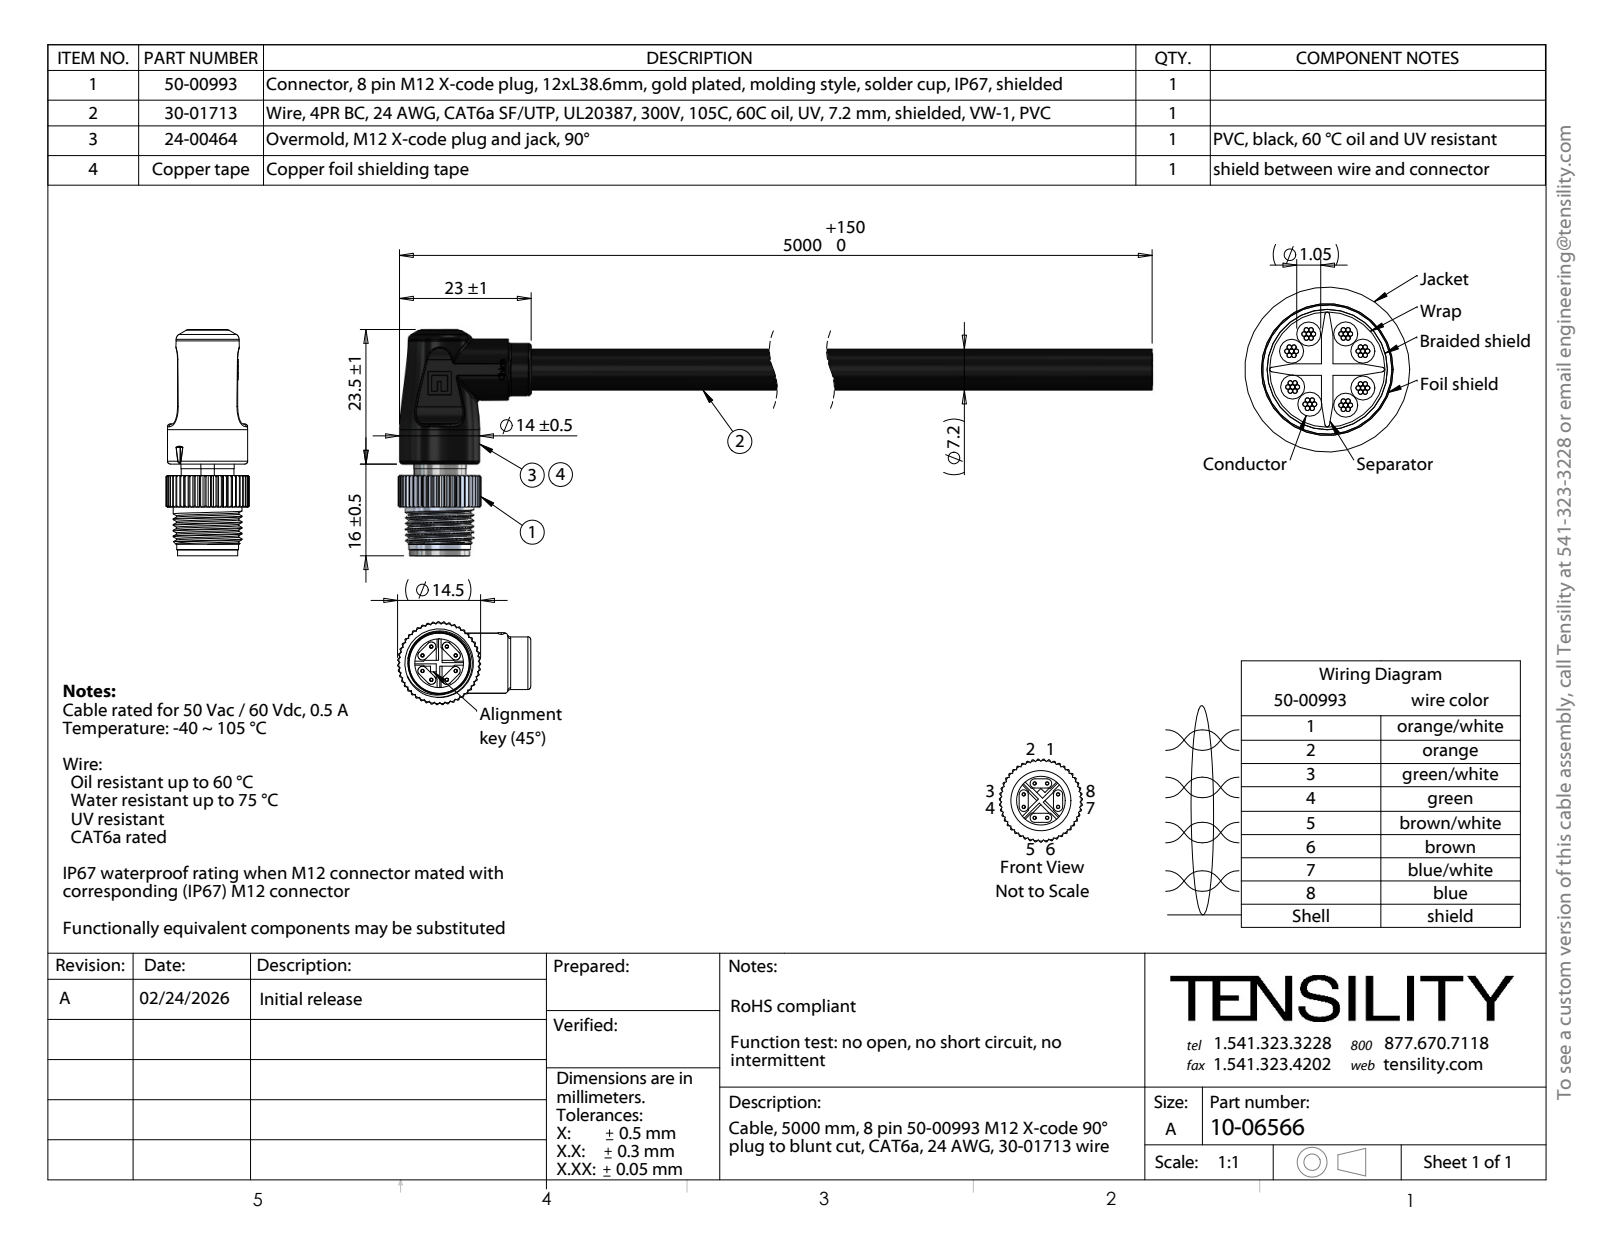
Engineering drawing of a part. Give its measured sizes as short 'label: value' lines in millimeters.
name: 50-00993-03; 50-00993-02; 30-01713_blunt cut; 50-00993-01_STEP (+5 more)
written by: SolidWorks 2025 (CONFIG_CONTROL_DESIGN)
unit: mm
bodies: 85 solids, 1492 faces (552 planar, 617 cylindrical, 323 other)
size: 173.25 × 39.5 × 14.49
volume: 10 489 mm³; area: 46 188 mm²
holes: 56× ⌀0.2, 8× ⌀0.6, 8× ⌀1.2, 1× ⌀2, 1× ⌀2.5, 1× ⌀5.03, 1× ⌀5.25, 1× ⌀5.65, 1× ⌀5.75, 1× ⌀7.5, 1× ⌀8.5, 1× ⌀9.07
bosses: 8× ⌀1.4, 8× ⌀1.15, 8× ⌀1.05, 8× ⌀0.8, 2× ⌀9.2, 1× ⌀14, 1× ⌀12, 1× ⌀11
rounds: 12× R0.1, 8× R0.8, 8× R1, 6× R0.5, 4× R2.17, 1× R7.25
face distances: 0.5, 2, 0.99, 0.98, 6, 5.5, 5, 16.25, 16.75, 0.7
hole spacings: 0.35, 1.61, 1.78, 3.19, 0.41, 1.06, 1.43, 1.93
